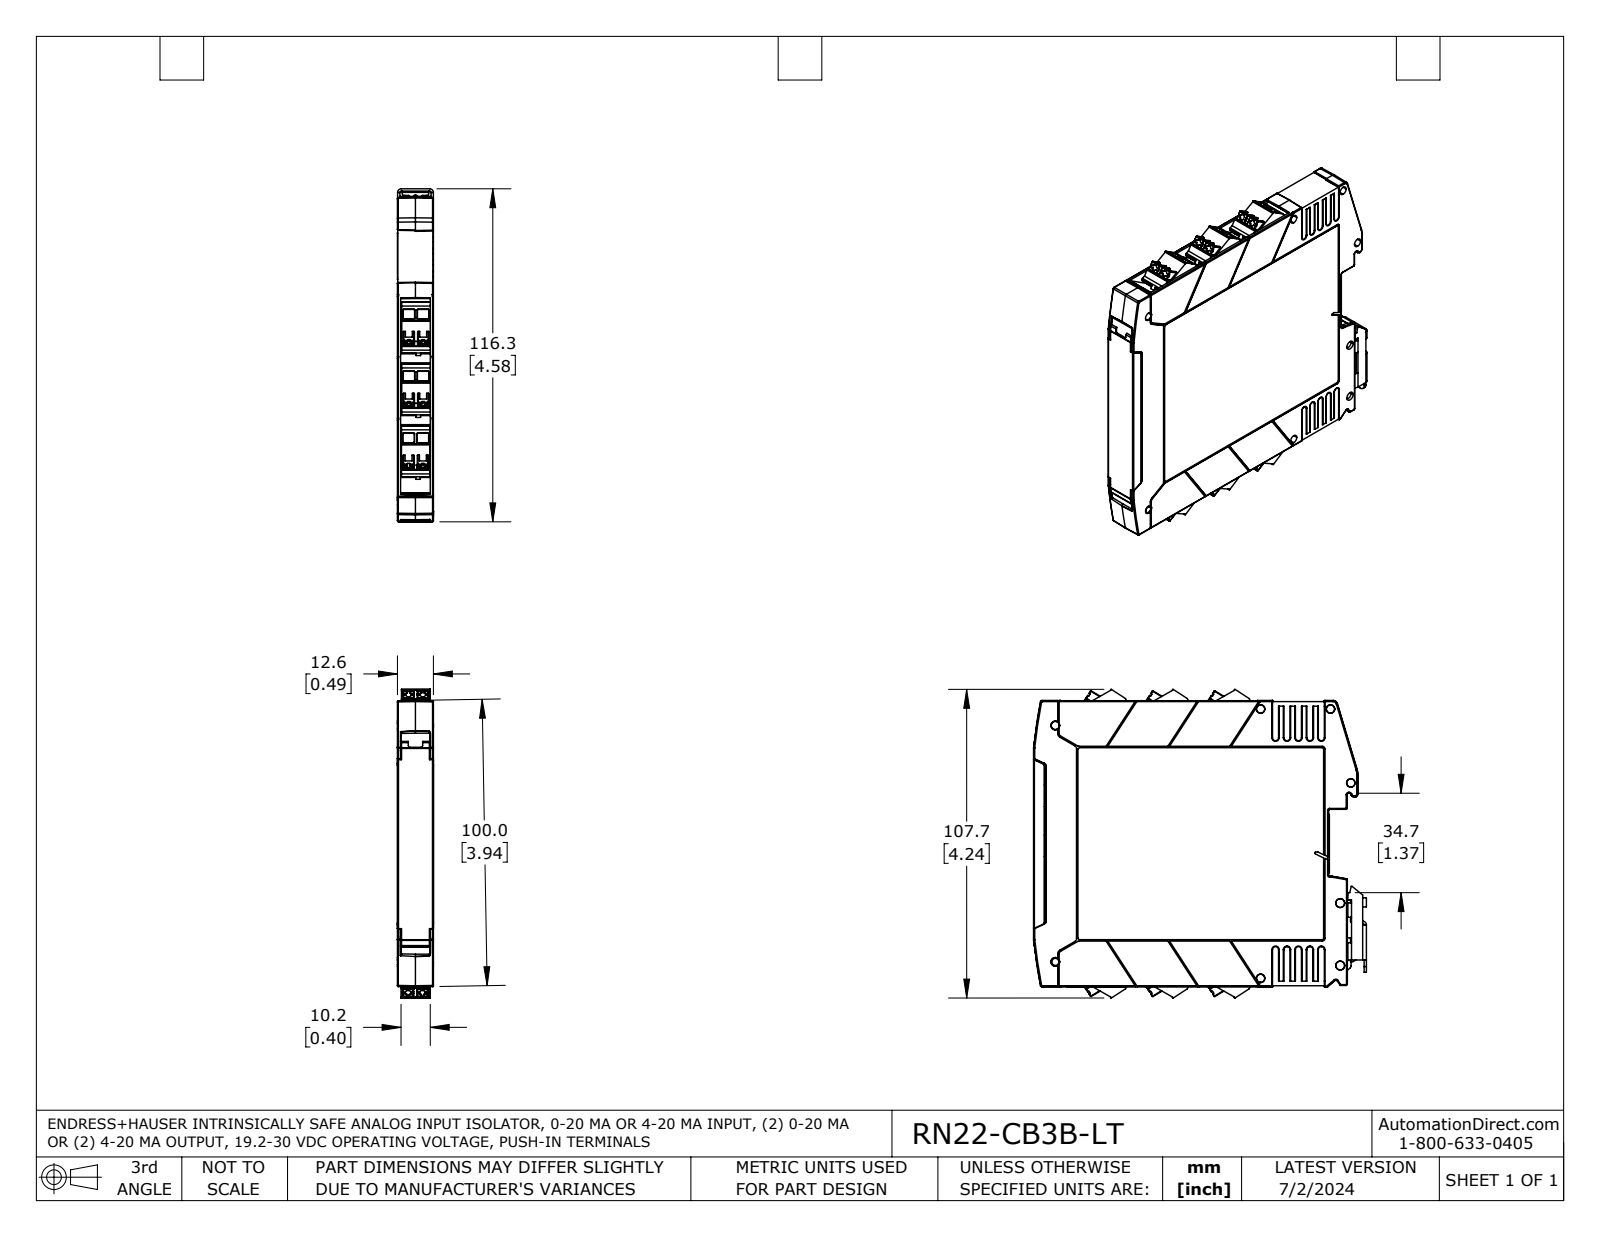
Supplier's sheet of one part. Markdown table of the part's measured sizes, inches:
| quantity | value |
| --- | --- |
| part name | RN22-CB3B-LT |
| STEP written by | SolidWorks 2021 (AUTOMOTIVE_DESIGN) |
| units | inches |
| bodies | 2 solids, 3045 faces (1939 planar, 765 cylindrical, 341 other) |
| overall size | 4.577 × 4.242 × 0.496 |
| volume | 8.127 in³ |
| surface area | 58.24 in² |
| round holes (diameter × count) | 0.118 × 3, 0.009 × 2, 0.097 × 1, 0.111 × 1 |
| partial cylindrical surfaces (radius × count) | 0.008 × 149, 0.02 × 71, 0.012 × 66, 0.039 × 28, 0.005 × 16, 0.114 × 12, 0.009 × 10, 0.024 × 10 |
| main face-to-face distances | 0.494, 0.043, 0.451, 0.039, 0.447, 0.047, 0.491, 0.435, 0.392, 0.031 |
| hole center spacings | 2.832, 4.477, 0.759, 0.76, 0.961, 2.073, 2.074, 3.031 |
